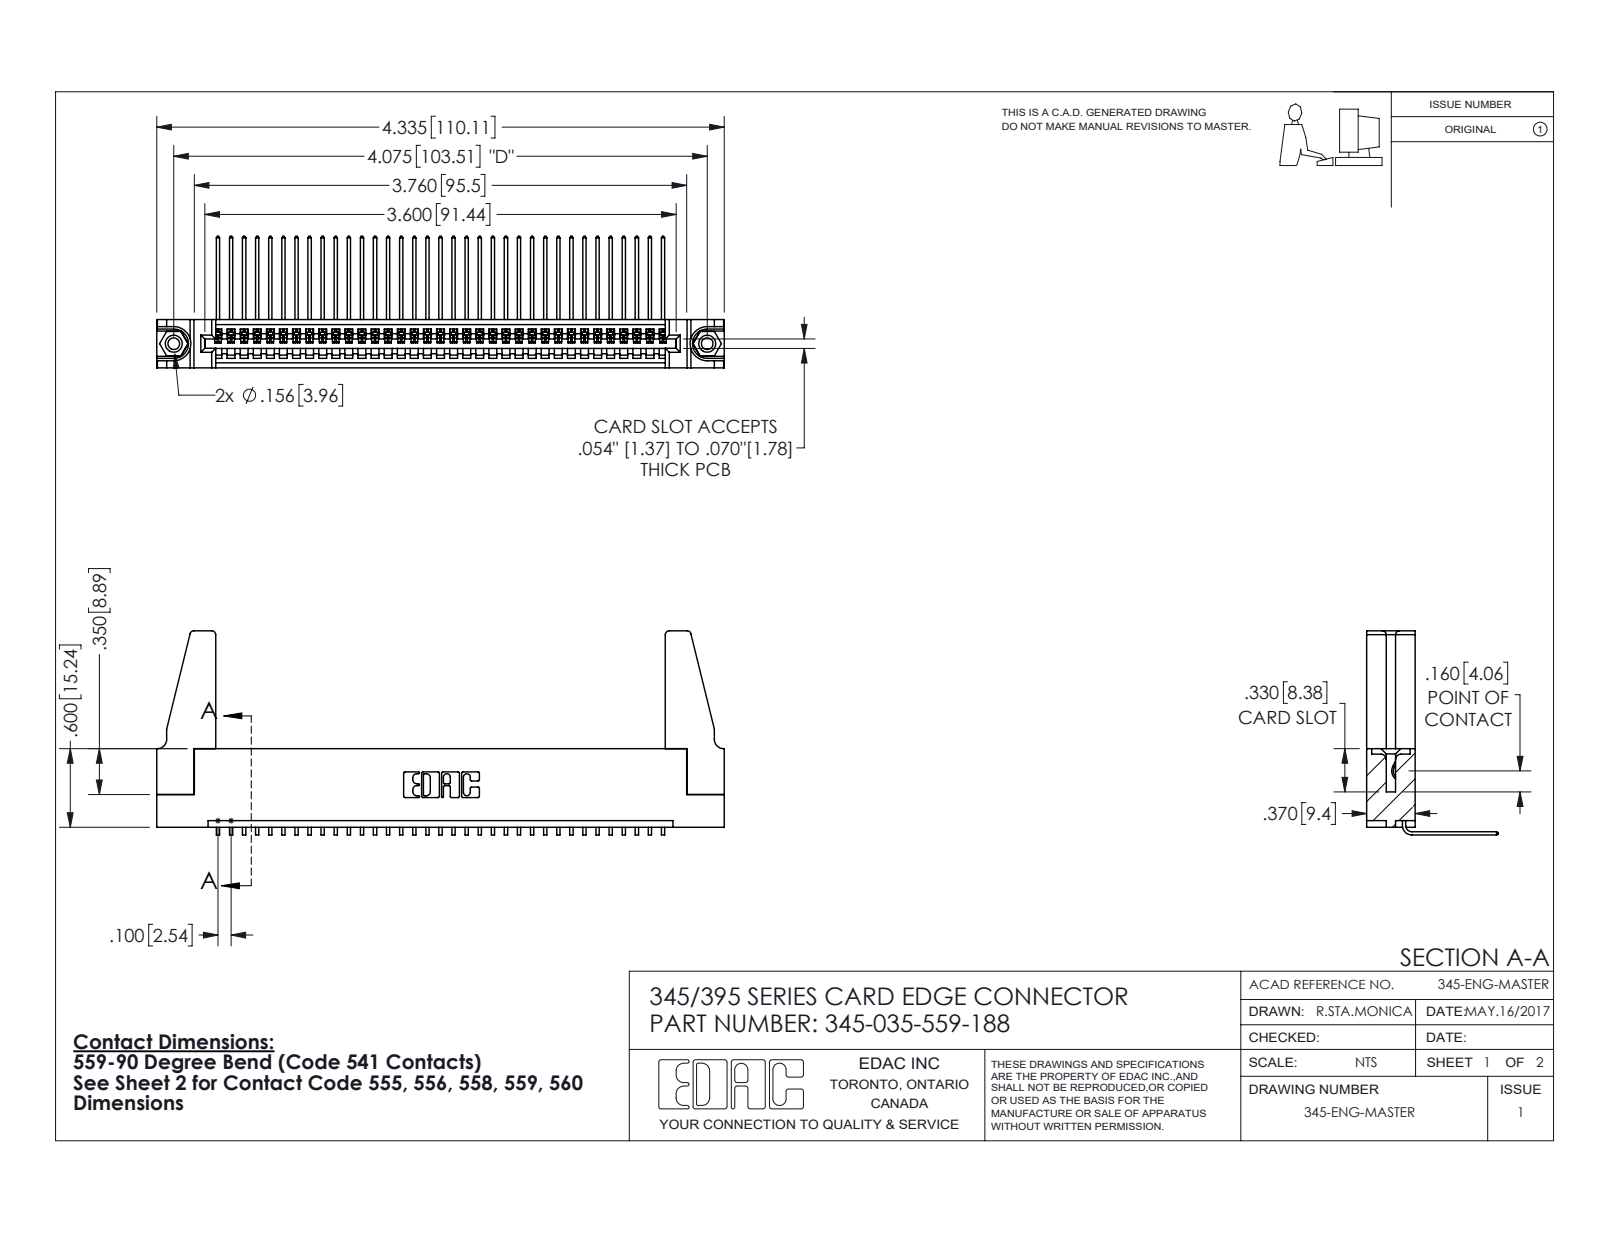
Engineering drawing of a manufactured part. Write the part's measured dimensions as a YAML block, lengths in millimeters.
part_name: "345-220-078_345-220-088; 345-292-001_558 559 Tail - 1; 345-035-559-188; 345-250-001_345-250-001-102 (+1 more)"
step_written_by: "SolidWorks 2016 (CONFIG_CONTROL_DESIGN)"
units: millimeters
bodies: {solids: 40, faces: 2350, planar: 1622, cylindrical: 712, other: 16}
overall_size: [110.1, 39.6, 25.5]
volume: 13800
surface_area: 17700
round_holes:
  - {diameter: 2.3, count: 2}
  - {diameter: 3.2, count: 2}
  - {diameter: 4, count: 2}
  - {diameter: 1.6, count: 1}
round_bosses_or_shafts:
  - {diameter: 3.9, count: 2}
partial_cylinders:
  - {radius: 0.2, count: 70}
  - {radius: 0.3, count: 22}
  - {radius: 0.8, count: 8}
  - {radius: 0.2, count: 6}
  - {radius: 0.8, count: 6}
  - {radius: 0.7, count: 3}
  - {radius: 0.8, count: 2}
  - {radius: 1, count: 2}
face_to_face_distances: [1.8, 9.4, 7.6, 5.1, 2.5, 6.9, 0.6, 5.7, 3.8, 1.8]
hole_center_spacings: [6.9, 97.5, 103.5]
